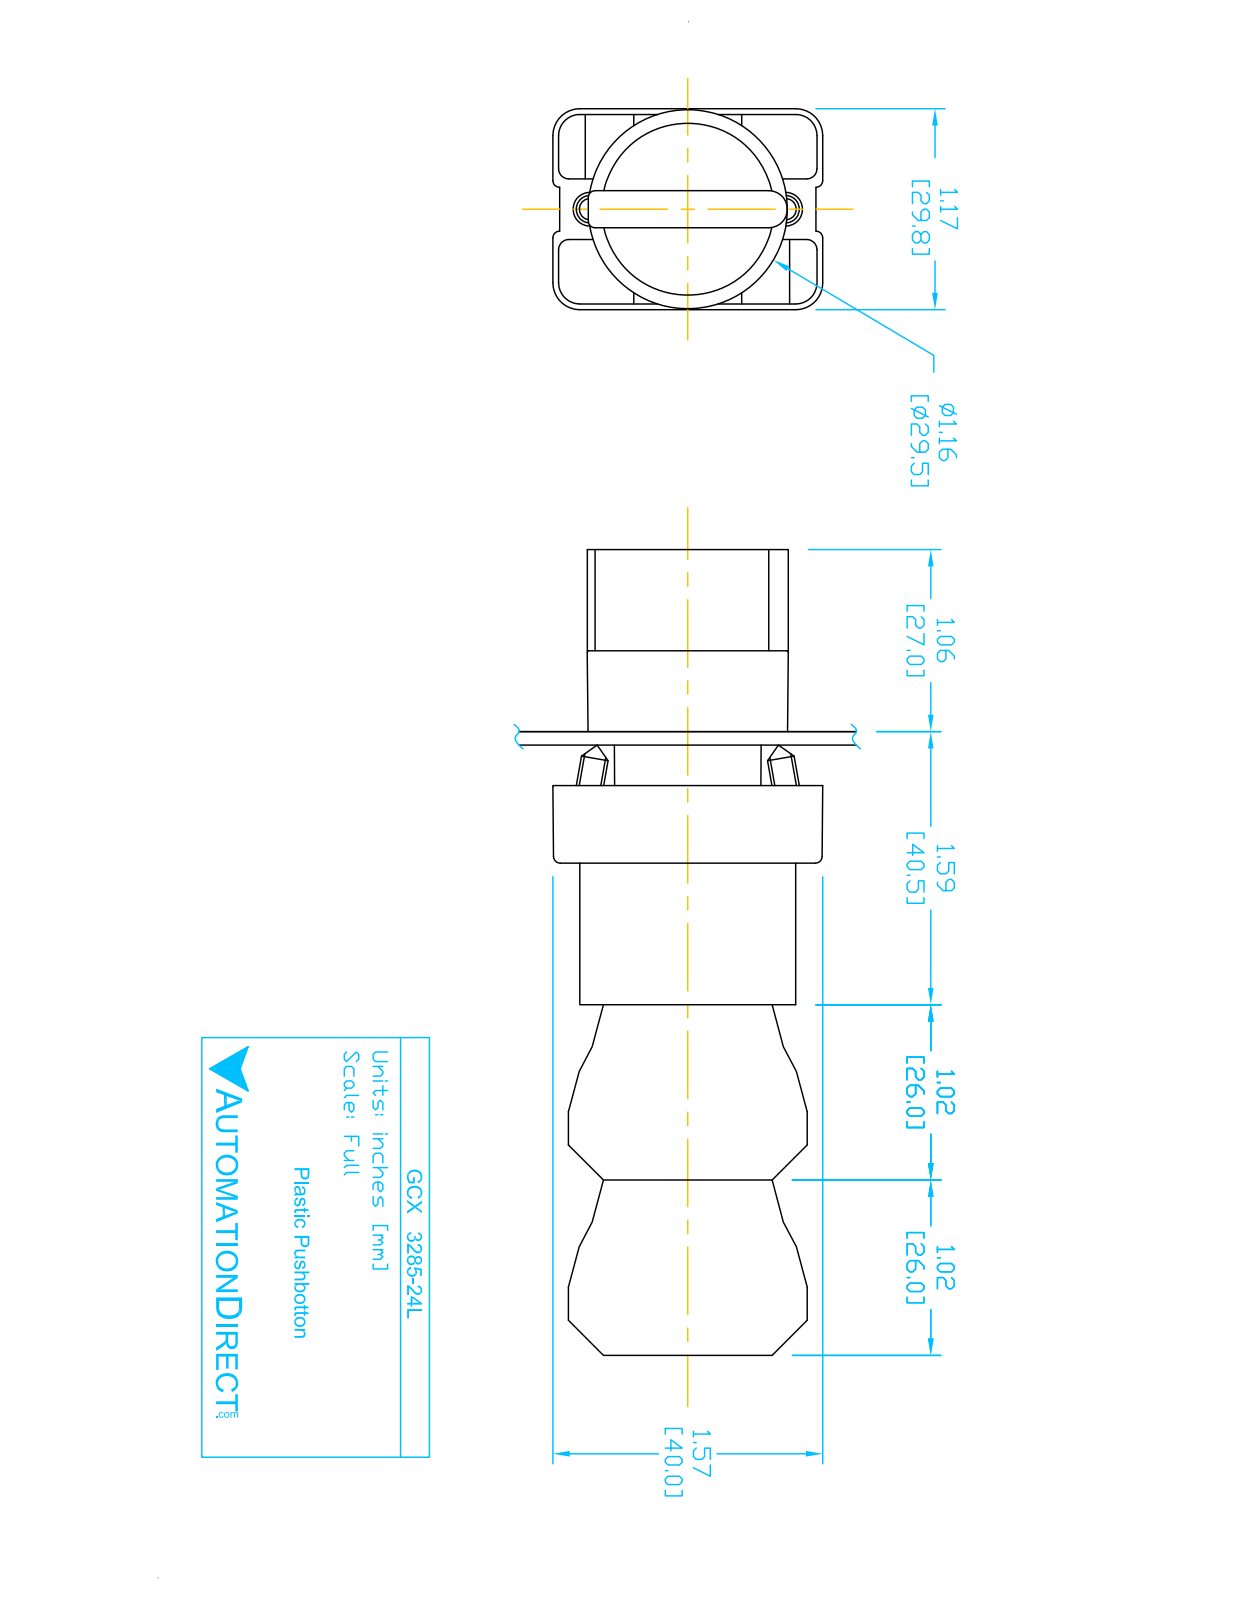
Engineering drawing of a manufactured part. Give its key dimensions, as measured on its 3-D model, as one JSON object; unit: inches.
{"part_name": "GCX3285L OPERATOR; ECX3029-2; ecx1030; ecx1040 (+2 more)", "step_written_by": "SolidWorks 2016 (AUTOMOTIVE_DESIGN)", "units": "inches", "bodies": {"solids": 11, "faces": 724, "planar": 488, "cylindrical": 193, "other": 43}, "overall_size": [4.677, 1.581, 1.177], "volume_in3": 4.751, "surface_area_in2": 59.22, "round_holes": [[0.079, 4], [0.087, 2], [0.124, 2], [0.13, 2], [0.197, 1], [0.469, 1], [0.878, 1], [0.888, 1], [1.024, 1]], "round_bosses_or_shafts": [[0.157, 4], [1.175, 1], [1.004, 1], [0.945, 1], [0.856, 1], [0.78, 1], [0.504, 1]], "partial_cylinders_radius": [[0.059, 24], [0.041, 12], [0.124, 12], [0.157, 12], [0.039, 9], [0.02, 2], [0.063, 2], [0.079, 2]], "face_to_face_distances": [0.579, 0.593, 1.024, 1.171, 0.014, 0.827, 1.85, 3.043, 2.02, 1.193], "hole_center_spacings": [0.236, 1.003, 0.974, 0.472, 0.539, 0.544, 1.083, 0.484]}
